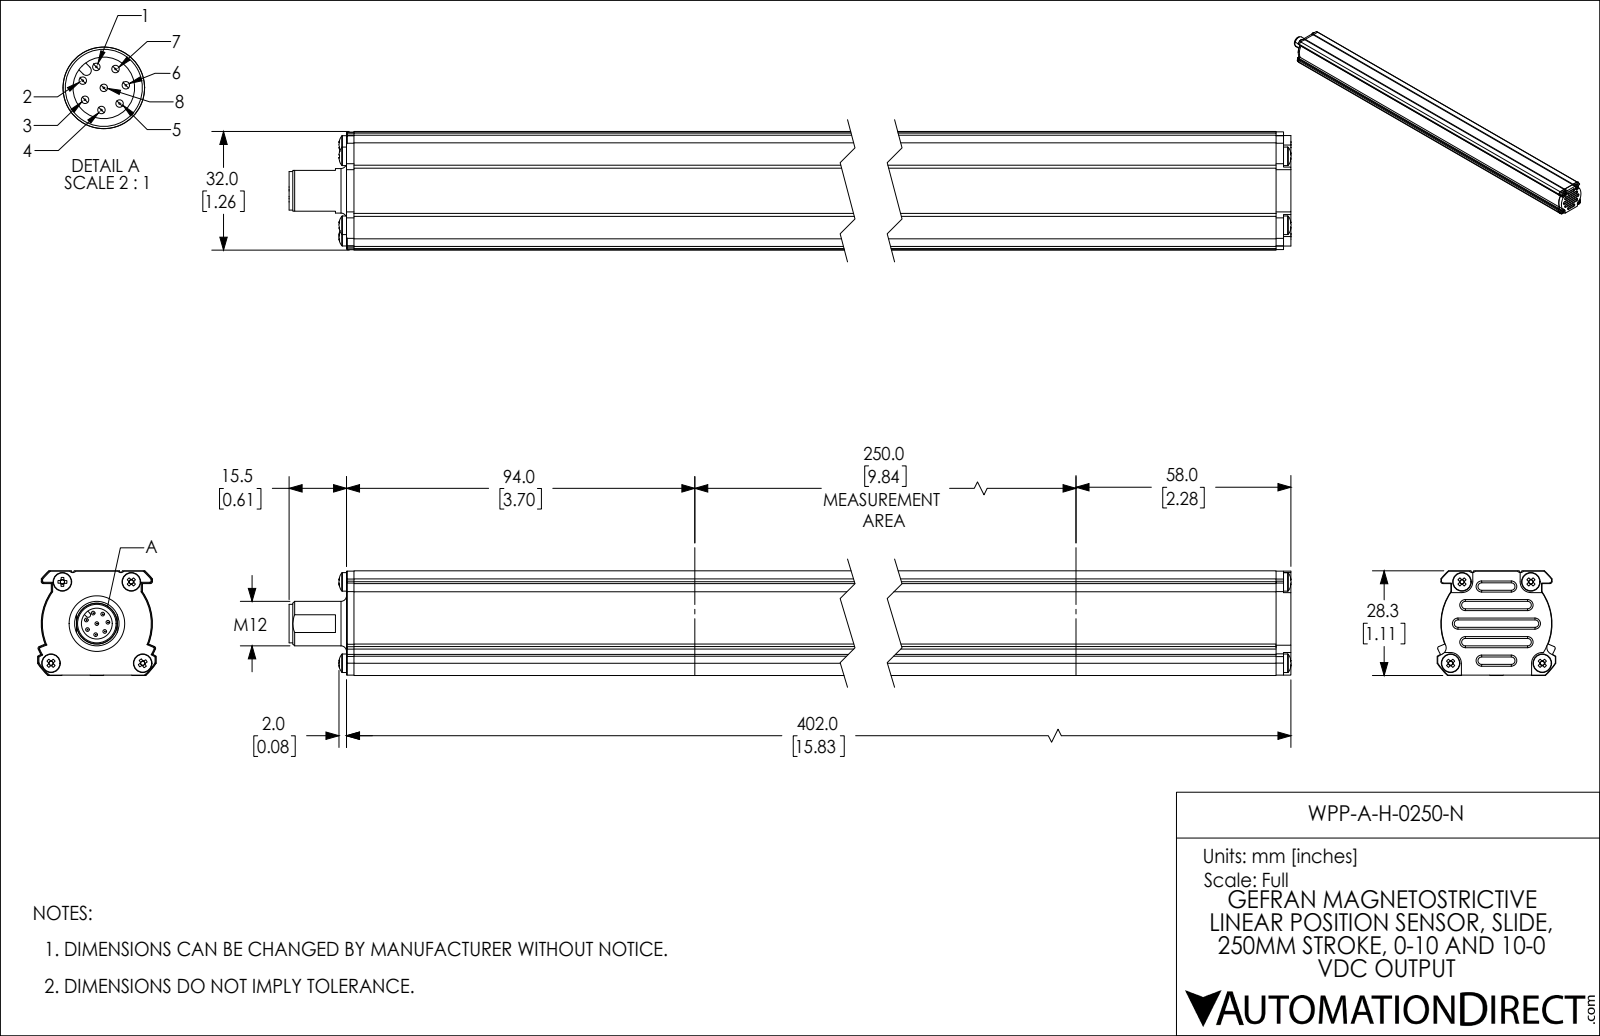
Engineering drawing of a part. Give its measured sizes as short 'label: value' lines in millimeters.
name: WPP-A-H-0250-N
written by: SolidWorks 2021 (CONFIG_CONTROL_DESIGN)
unit: mm
bodies: 20 solids, 573 faces (301 planar, 131 cylindrical, 141 other)
size: 417.6 × 32 × 28.2
volume: 321 000 mm³; area: 68 900 mm²
holes: 4× ⌀2.3, 4× ⌀2.6, 1× ⌀7, 1× ⌀8.3, 1× ⌀9.4
bosses: 8× ⌀1, 4× ⌀5, 1× ⌀12, 1× ⌀10.4, 1× ⌀9.6, 1× ⌀8
rounds: 8× R0.5, 4× R2.9, 2× R0.4, 2× R1, 2× R1.9, 1× R0.7, 1× R2, 1× R14.9
face distances: 28, 28.2, 24.8, 24.6, 3.5, 396, 3.7, 28.3, 2, 398
hole spacings: 14.6, 16.4, 18.6, 22.1, 22.2, 24.7, 30.8, 30.9
